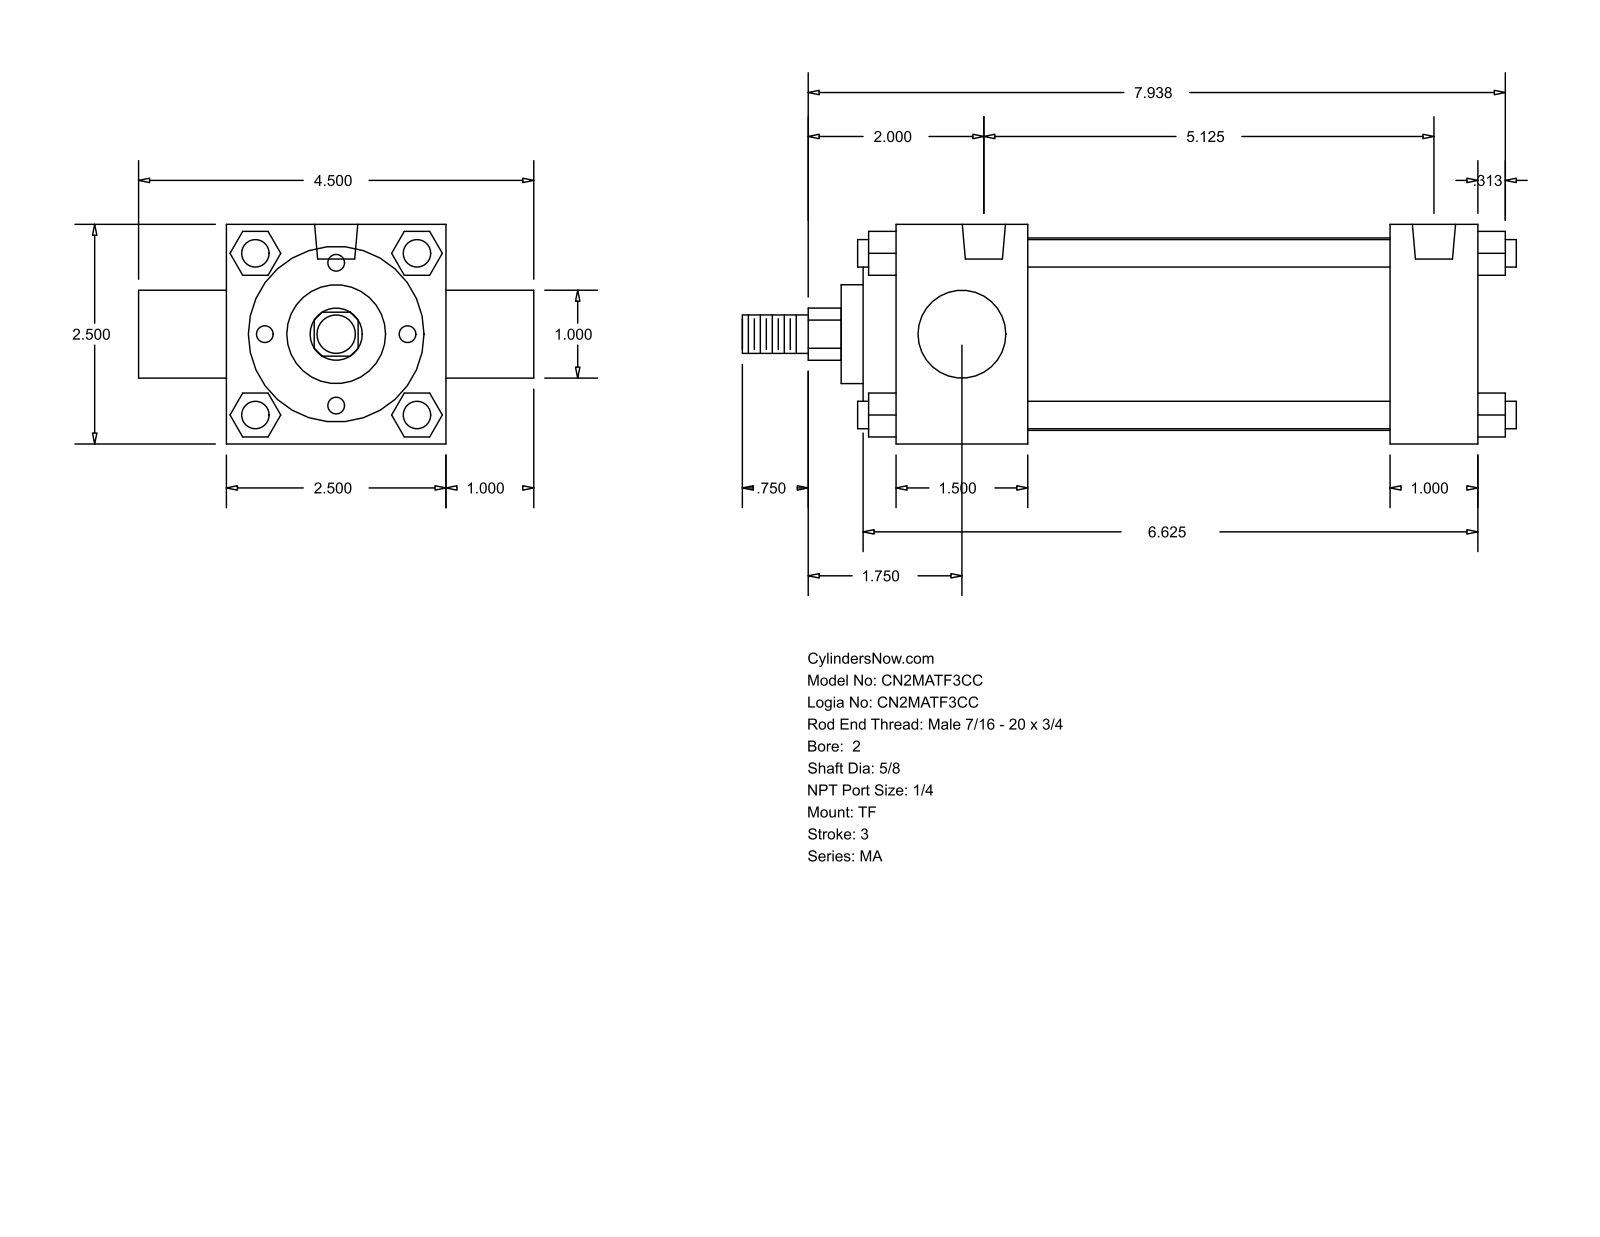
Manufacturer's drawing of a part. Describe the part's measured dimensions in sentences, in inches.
The part is named "MA_TF__0200_0.625". Its 3-D file was written by "GSSL Pune (CONFIG_CONTROL_DESIGN)". It is 0 solids with 122 faces: 93 planar, 29 cylindrical and 0 other. Overall it measures 8.813 by 4.5 by 2.5 inches. Round holes: 3 of diameter 0.313, 2 of diameter 0.492. Round bosses or shafts: 4 of diameter 0.313, 1 of diameter 2.19, 1 of diameter 2, 1 of diameter 1.125, 1 of diameter 1, 1 of diameter 0.625, 1 of diameter 0.437. Partial cylindrical surfaces (rounded edges, fillets, slot ends): 1 of radius 0.297. The main face-to-face distances are 2.5, 1, 1.5, 6.625, 0.5, 5.625, 4.125, 5.125, 0.375, 1.875. The hole center spacings are 5.125.
